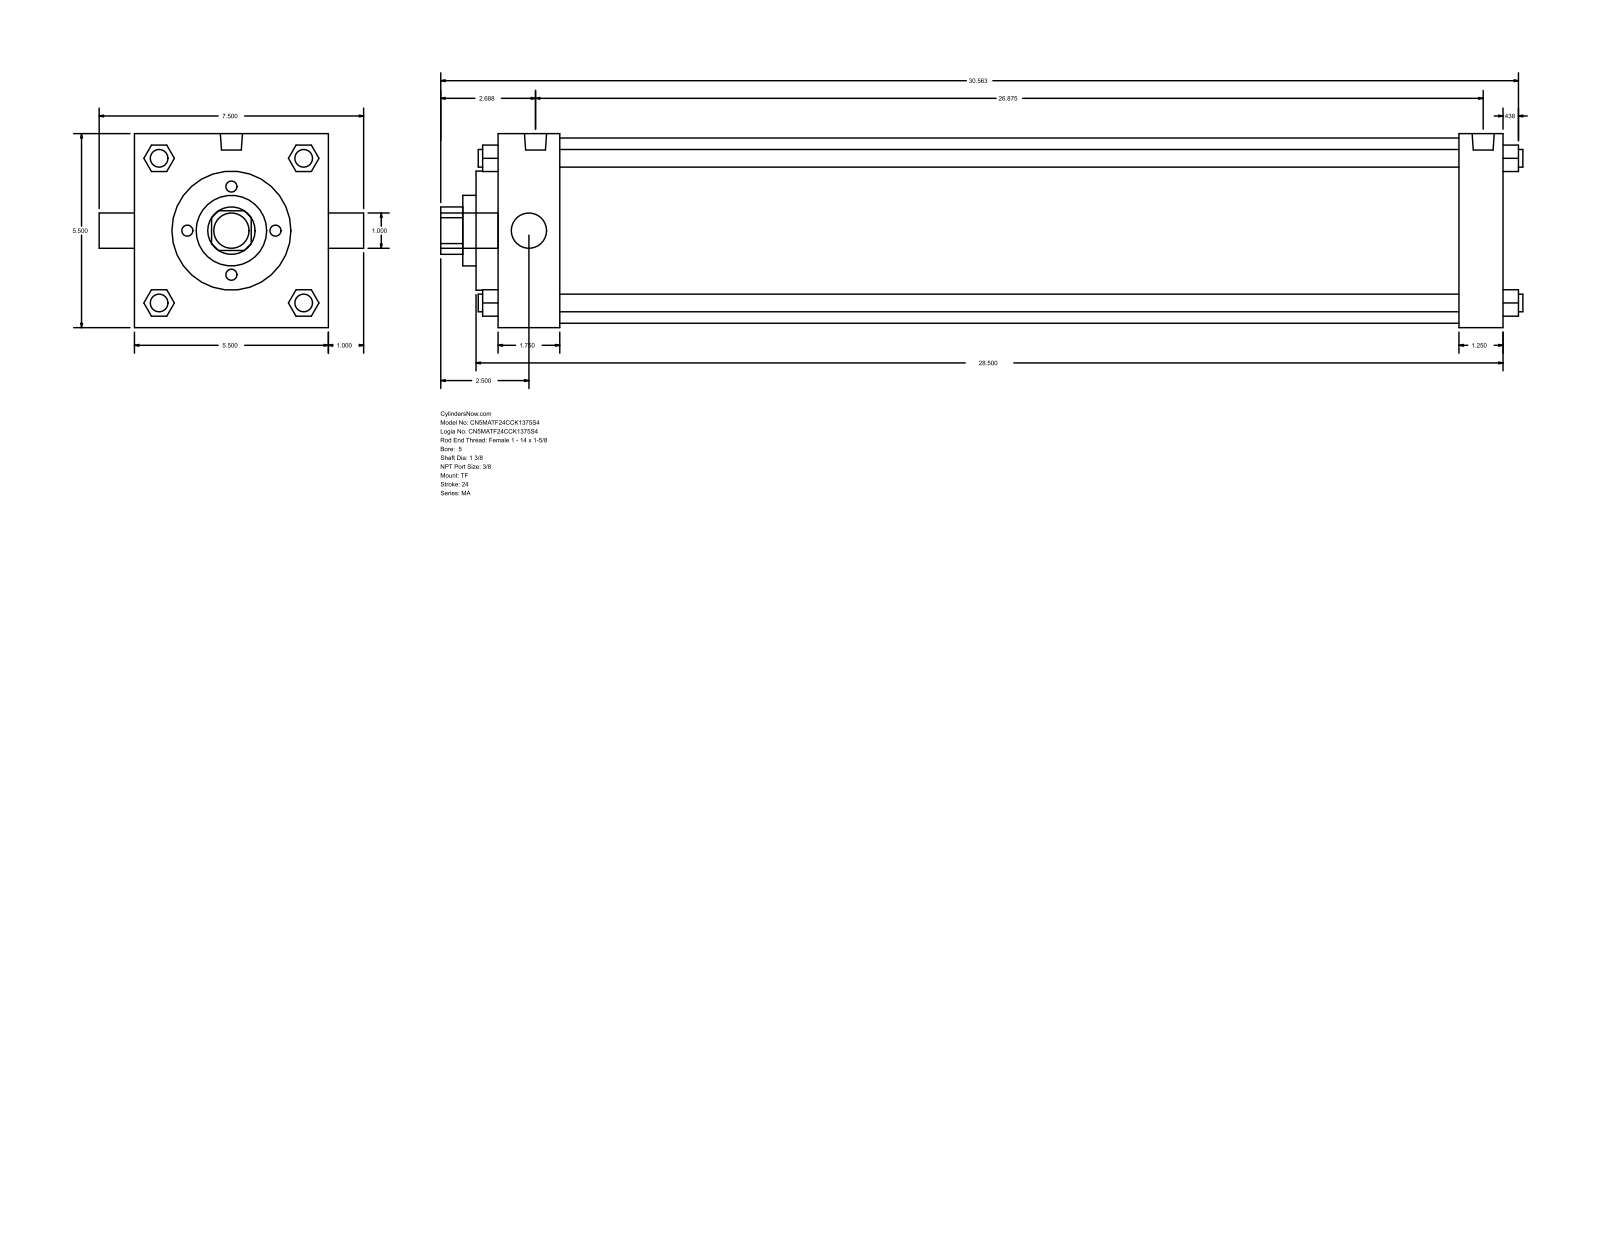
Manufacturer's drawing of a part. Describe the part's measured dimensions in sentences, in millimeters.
The part is named "MA_TF__0500_1.375". Its 3-D file was written by "GSSL Pune (CONFIG_CONTROL_DESIGN)". It is 0 solids with 122 faces: 93 planar, 29 cylindrical and 0 other. Overall it measures 779.46 by 190.5 by 139.7 millimeters. Round holes: 1 of diameter 25.4, 1 of diameter 34.92, 1 of diameter 50.8, 1 of diameter 85.72, 1 of diameter 133.35. Round bosses or shafts: 4 of diameter 12.7, 3 of diameter 11.11, 2 of diameter 15.93, 1 of diameter 25.4. Partial cylindrical surfaces (rounded edges, fillets, slot ends): 1 of radius 17.06. The main face-to-face distances are 139.7, 723.9, 692.15, 31.75, 44.45, 647.7, 679.45, 15.87, 60.32, 708.02.
